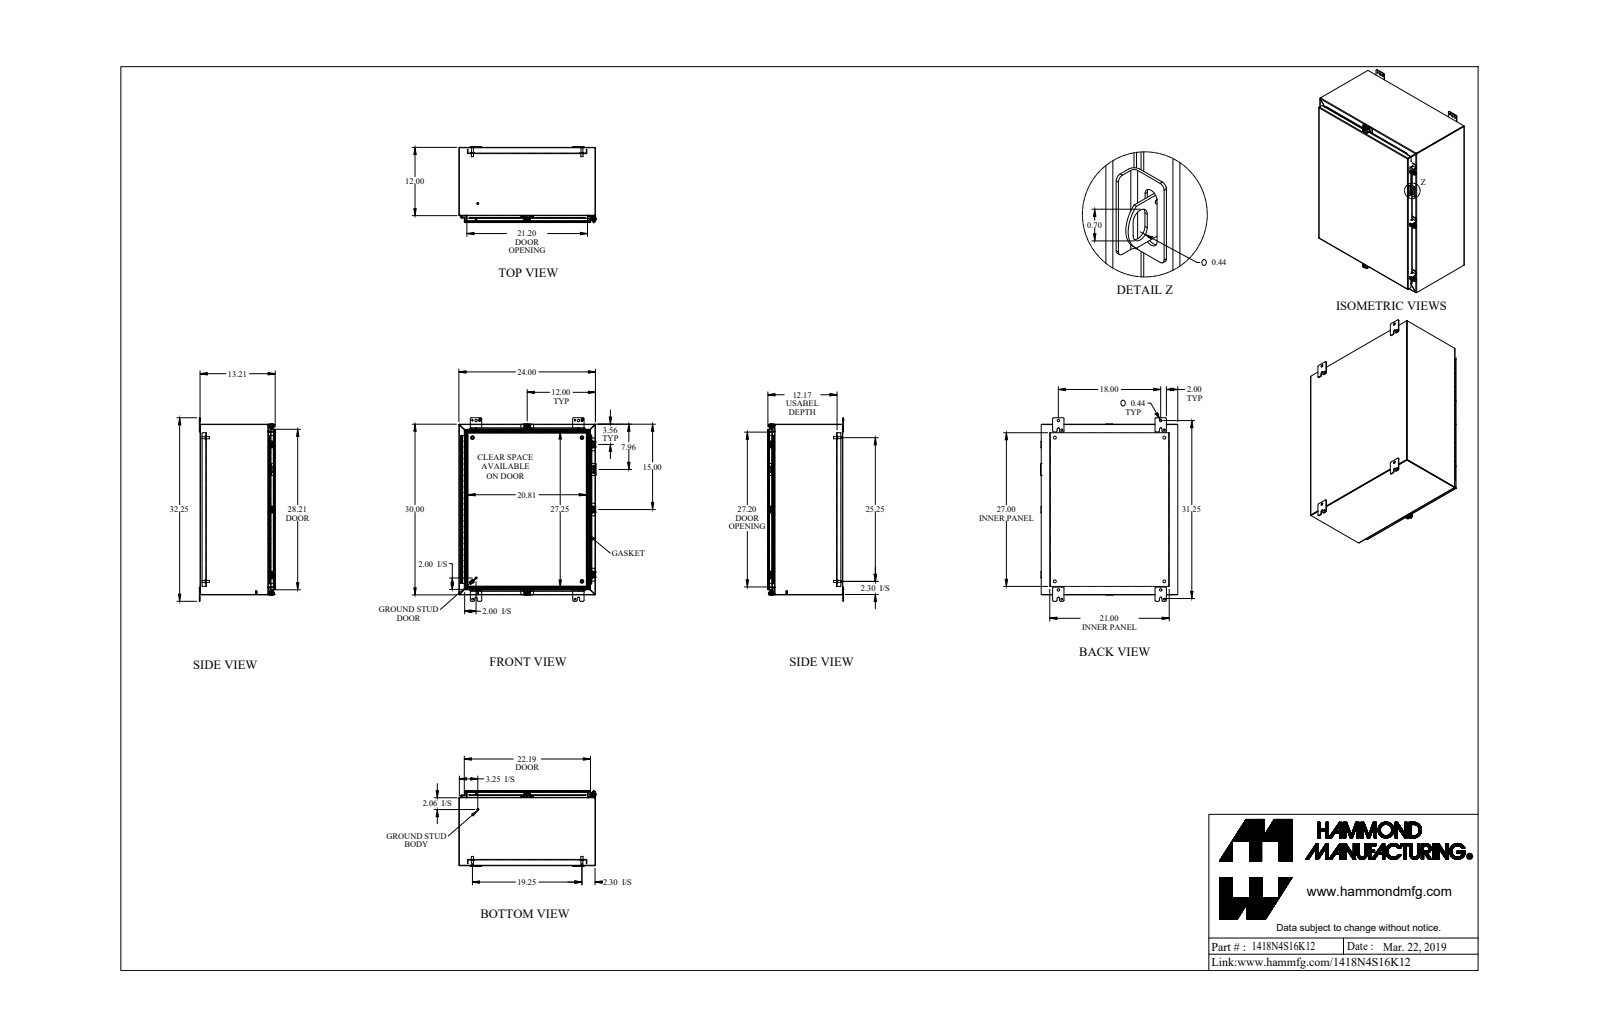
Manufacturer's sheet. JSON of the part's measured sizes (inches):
{"part_name": "1418N4S16K12_Default", "step_written_by": "SolidWorks 2019 (CONFIG_CONTROL_DESIGN)", "units": "inches", "bodies": {"solids": 45, "faces": 1503, "planar": 803, "cylindrical": 568, "other": 132}, "overall_size": [32.25, 24.126, 13.375], "volume_in3": 288.4, "surface_area_in2": 7623, "round_holes": [[0.213, 5], [0.265, 5], [0.375, 5], [0.313, 4], [0.437, 4], [0.5, 4], [0.307, 2], [0.445, 2], [0.11, 1], [0.125, 1]], "round_bosses_or_shafts": [[0.5, 5], [0.39, 5], [0.244, 5], [0.65, 4], [0.375, 4], [0.332, 4], [1, 2], [0.313, 2]], "partial_cylinders_radius": [[0.25, 28], [0.048, 27], [0.143, 27], [0.188, 26], [0.036, 22], [0.108, 22], [0.125, 12], [0.141, 10]], "face_to_face_distances": [0.072, 23.928, 0.072, 13.066, 13.138, 13.138, 13.21, 0.095, 29.928, 12.106], "hole_center_spacings": [29.018, 9.857, 18, 25.25, 31.751, 2.434, 3.065, 9.857]}
